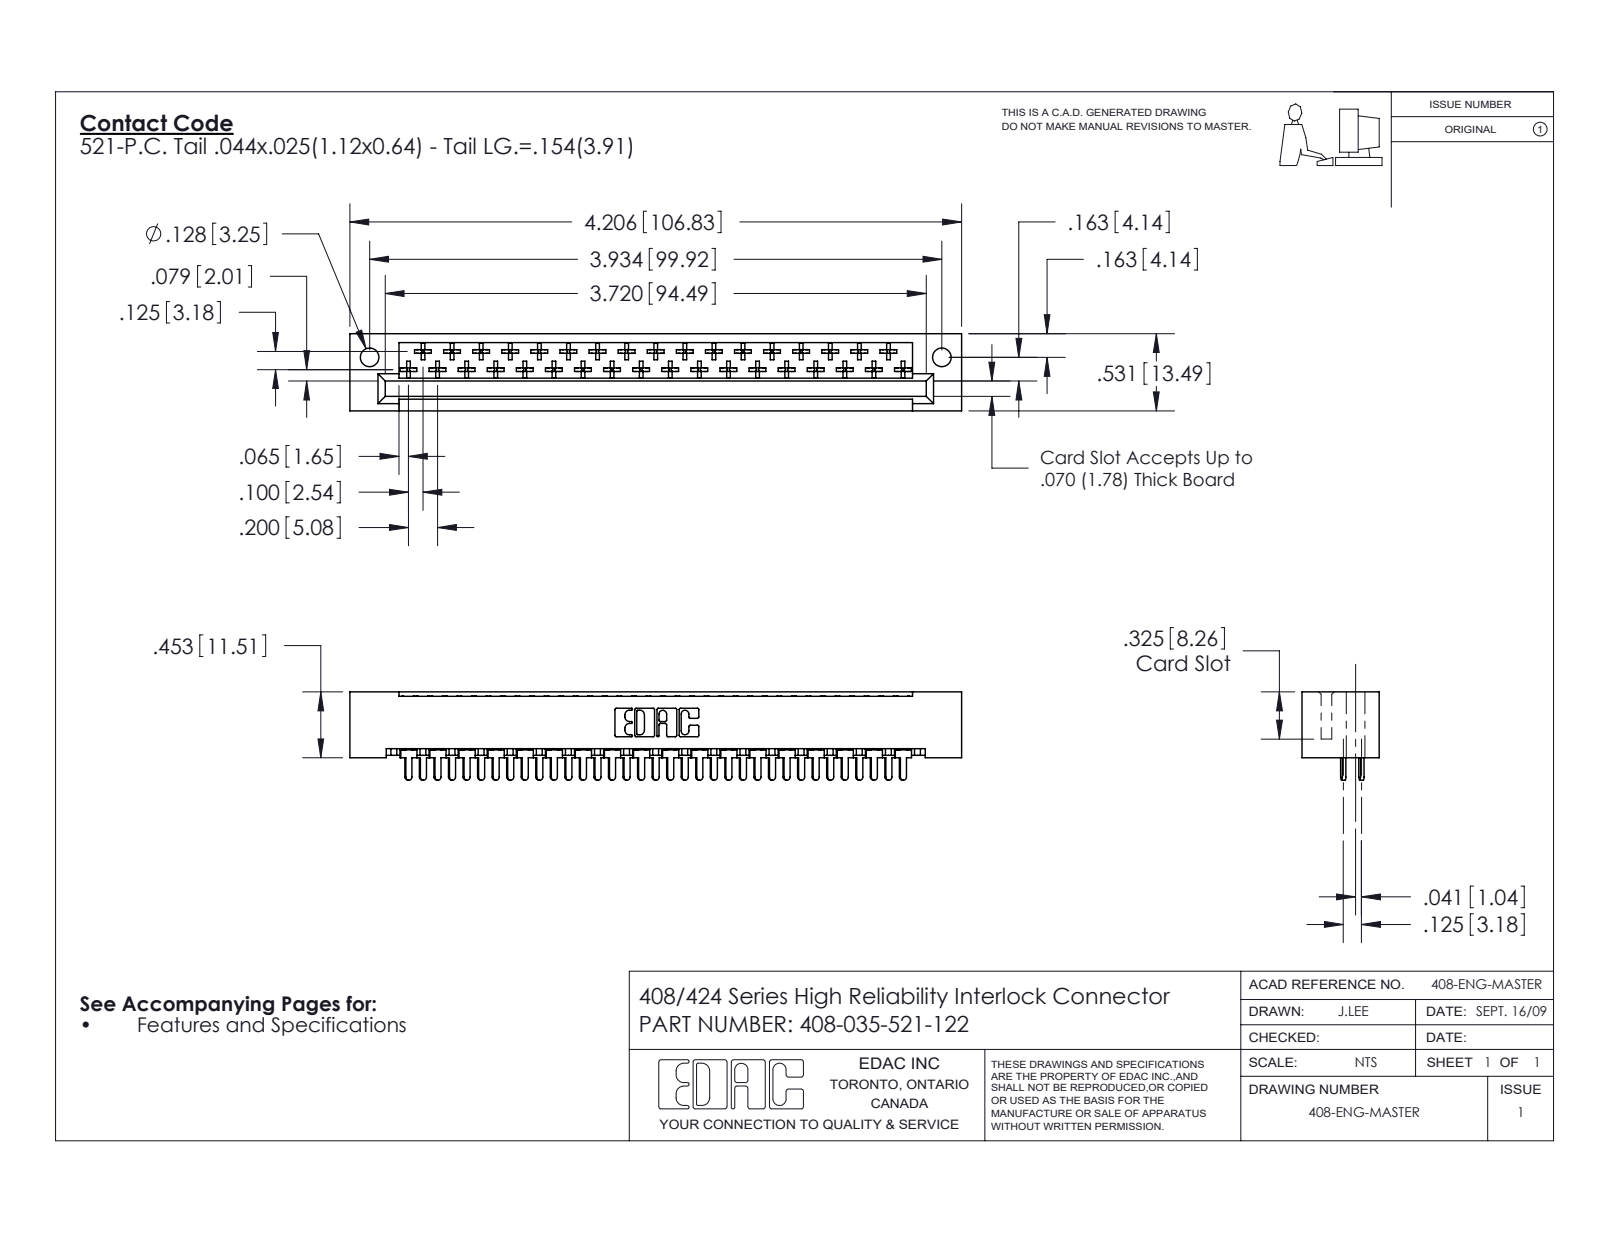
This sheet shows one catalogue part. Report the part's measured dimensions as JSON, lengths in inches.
{"part_name": "408 Part_035 - 1; 408-035-521-122; 408-290-001_408-290-121", "step_written_by": "SolidWorks 2016 (CONFIG_CONTROL_DESIGN)", "units": "inches", "bodies": {"solids": 36, "faces": 2052, "planar": 1549, "cylindrical": 363, "other": 140}, "overall_size": [4.206, 0.607, 0.531], "volume_in3": 0.712, "surface_area_in2": 22.51, "round_holes": [[0.128, 2]], "partial_cylinders_radius": [[0.01, 210], [0.02, 37], [0.022, 35], [0.01, 22], [0.007, 6], [0.031, 6], [0.026, 3]], "face_to_face_distances": [0.1, 0.296, 0.531, 0.025, 0.125, 0.025, 0.272, 0.235, 0.259, 0.135], "hole_center_spacings": [3.934]}
